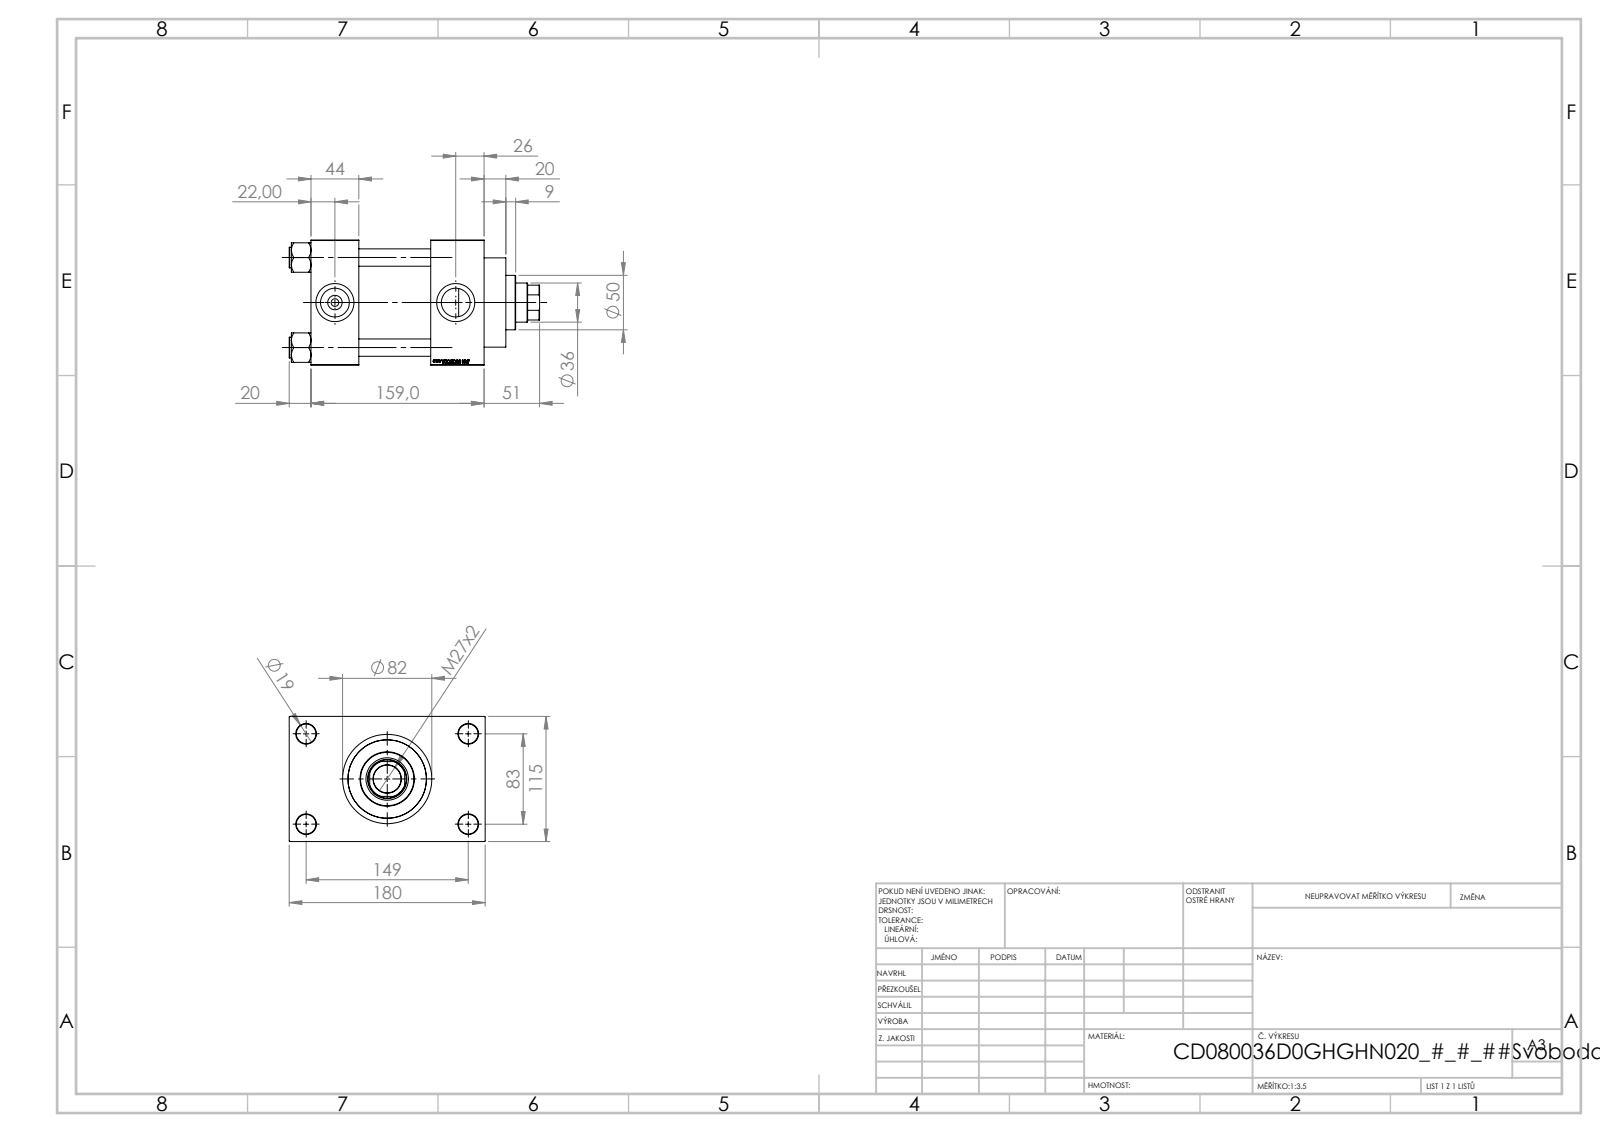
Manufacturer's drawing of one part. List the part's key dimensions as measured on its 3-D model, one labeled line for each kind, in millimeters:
Part name (STEP PRODUCT): V215CD_VCP_D; V215CD_D_TYCINKA; V215CD_D_Body; V215CD_VC_A (+1 more)
STEP written by: SolidWorks 2019 (CONFIG_CONTROL_DESIGN)
Units: millimetres
Bodies: 11 solids, 1151 faces (545 planar, 88 cylindrical, 518 other)
Overall size (bounding box): 230 × 180 × 115
Volume: 1 979 000 mm³ · Surface area: 296 594 mm²
Round holes (diameter × count): ⌀16 ×4, ⌀18 ×4, ⌀7 ×2, ⌀26.44 ×2, ⌀35 ×2, ⌀25.5 ×1, ⌀36 ×1, ⌀39 ×1, ⌀61 ×1, ⌀72 ×1, ⌀80 ×1
Round bosses / shafts (diameter × count): ⌀19 ×4, ⌀86 ×1, ⌀82 ×1, ⌀50 ×1
Partial cylindrical surfaces — rounded edges, fillets, slot ends (radius × count): R17.5 ×1
Main face-to-face distances: 115, 66, 110, 49, 44, 159, 32.5, 147.5, 20, 69
Hole centre spacings: 33.15, 58.48, 82.7, 85.28, 89.24, 115.85, 142.43, 83
